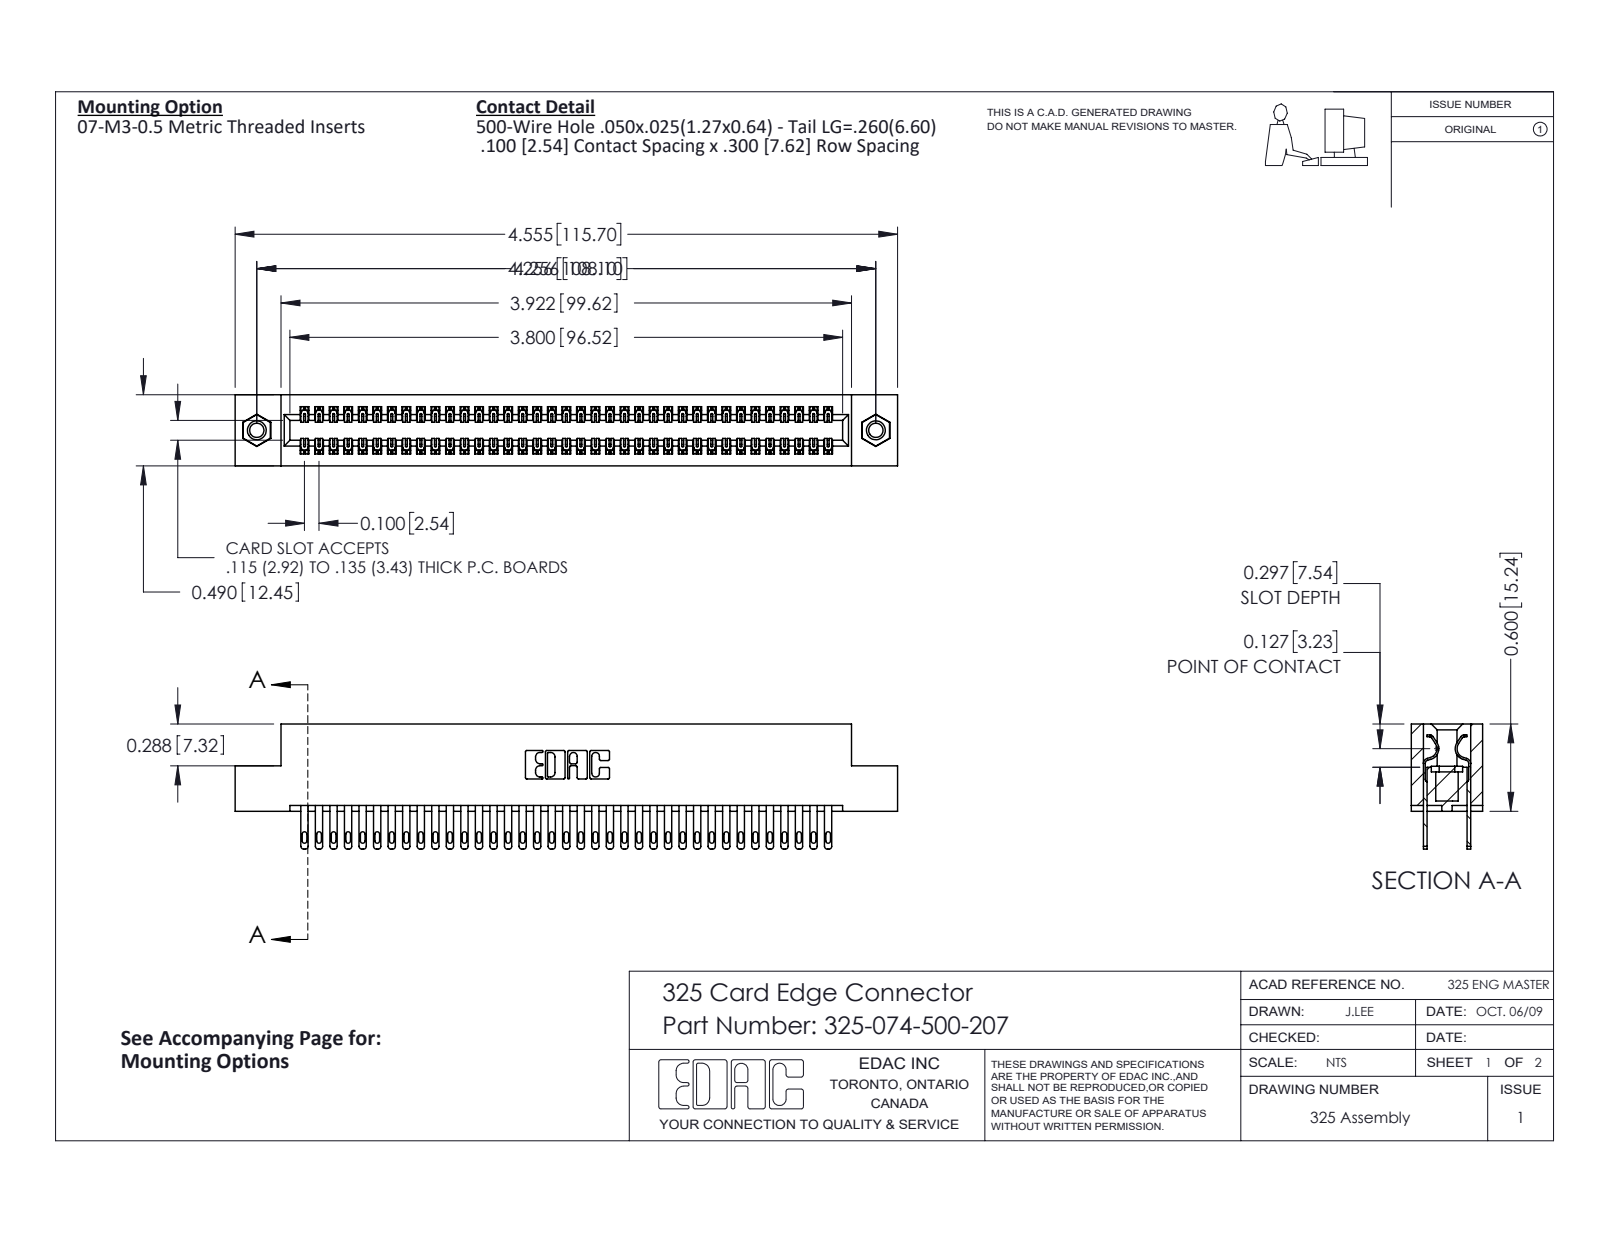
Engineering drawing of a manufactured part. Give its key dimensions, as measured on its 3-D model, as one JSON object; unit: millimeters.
{"part_name": "325-292-001_325-293-100; 325-074-500-207; 345-250-001_345-250-005-103; 325 Part_TI", "step_written_by": "SolidWorks 2016 (CONFIG_CONTROL_DESIGN)", "units": "millimeters", "bodies": {"solids": 77, "faces": 3726, "planar": 2322, "cylindrical": 1388, "other": 16}, "overall_size": [115.7, 21.8, 12.4], "volume_mm3": 15100, "surface_area_mm2": 18960, "round_holes": [[2.5, 2], [3.2, 2], [4.1, 2]], "round_bosses_or_shafts": [[3.9, 2]], "partial_cylinders_radius": [[0.2, 111], [0.4, 74], [0.5, 74], [0.3, 22], [0.2, 6], [0.8, 6], [0.7, 3], [0.4, 2]], "face_to_face_distances": [2.1, 10.3, 7.6, 2.7, 9.7, 0.6, 12.4, 8.3, 7, 14.2], "hole_center_spacings": [108.1]}
